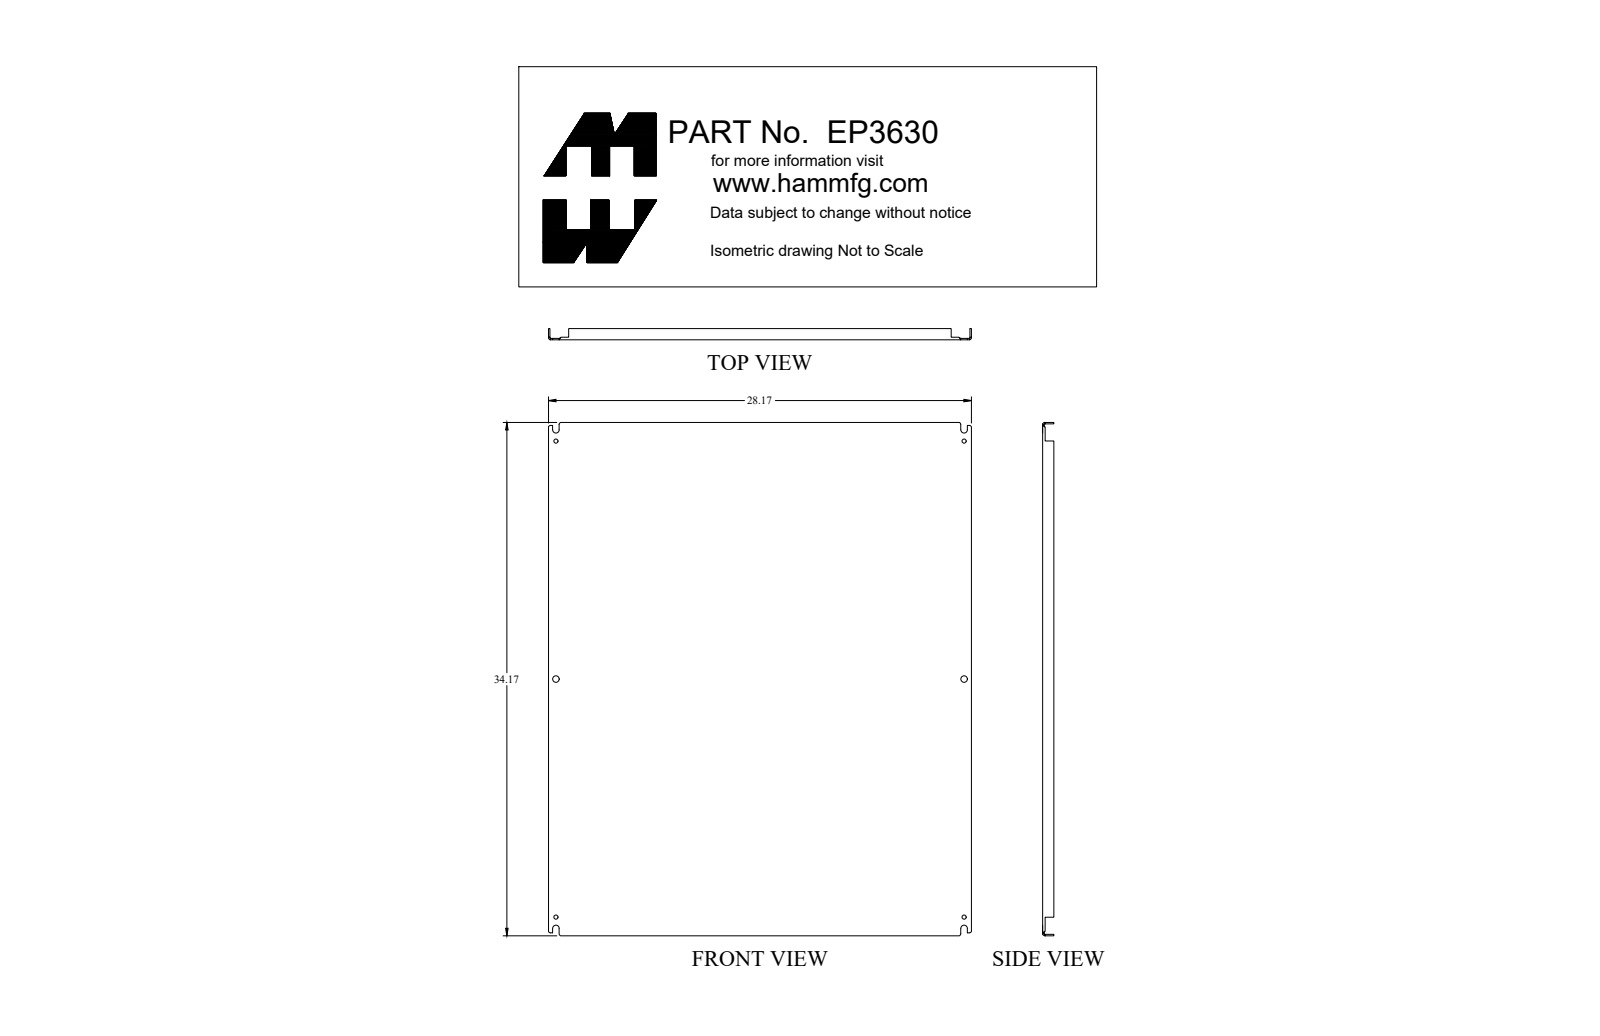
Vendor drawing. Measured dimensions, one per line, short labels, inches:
name: EP3630
written by: SolidWorks 2018 (AUTOMOTIVE_DESIGN)
unit: in
bodies: 1 solid, 132 faces (74 planar, 42 cylindrical, 16 other)
size: 34.17 × 28.17 × 0.75
volume: 97.94 in³; area: 2 075 in²
holes: 4× ⌀0.281, 2× ⌀0.437
rounds: 4× R0.048, 4× R0.063, 4× R0.143, 4× R0.219
face distances: 0.095, 28.075, 34.075, 28.17, 27.98, 34.17, 33.98, 0.75, 0.655, 0.171
hole spacings: 15.844, 31.468, 27.188, 31.688, 41.753
